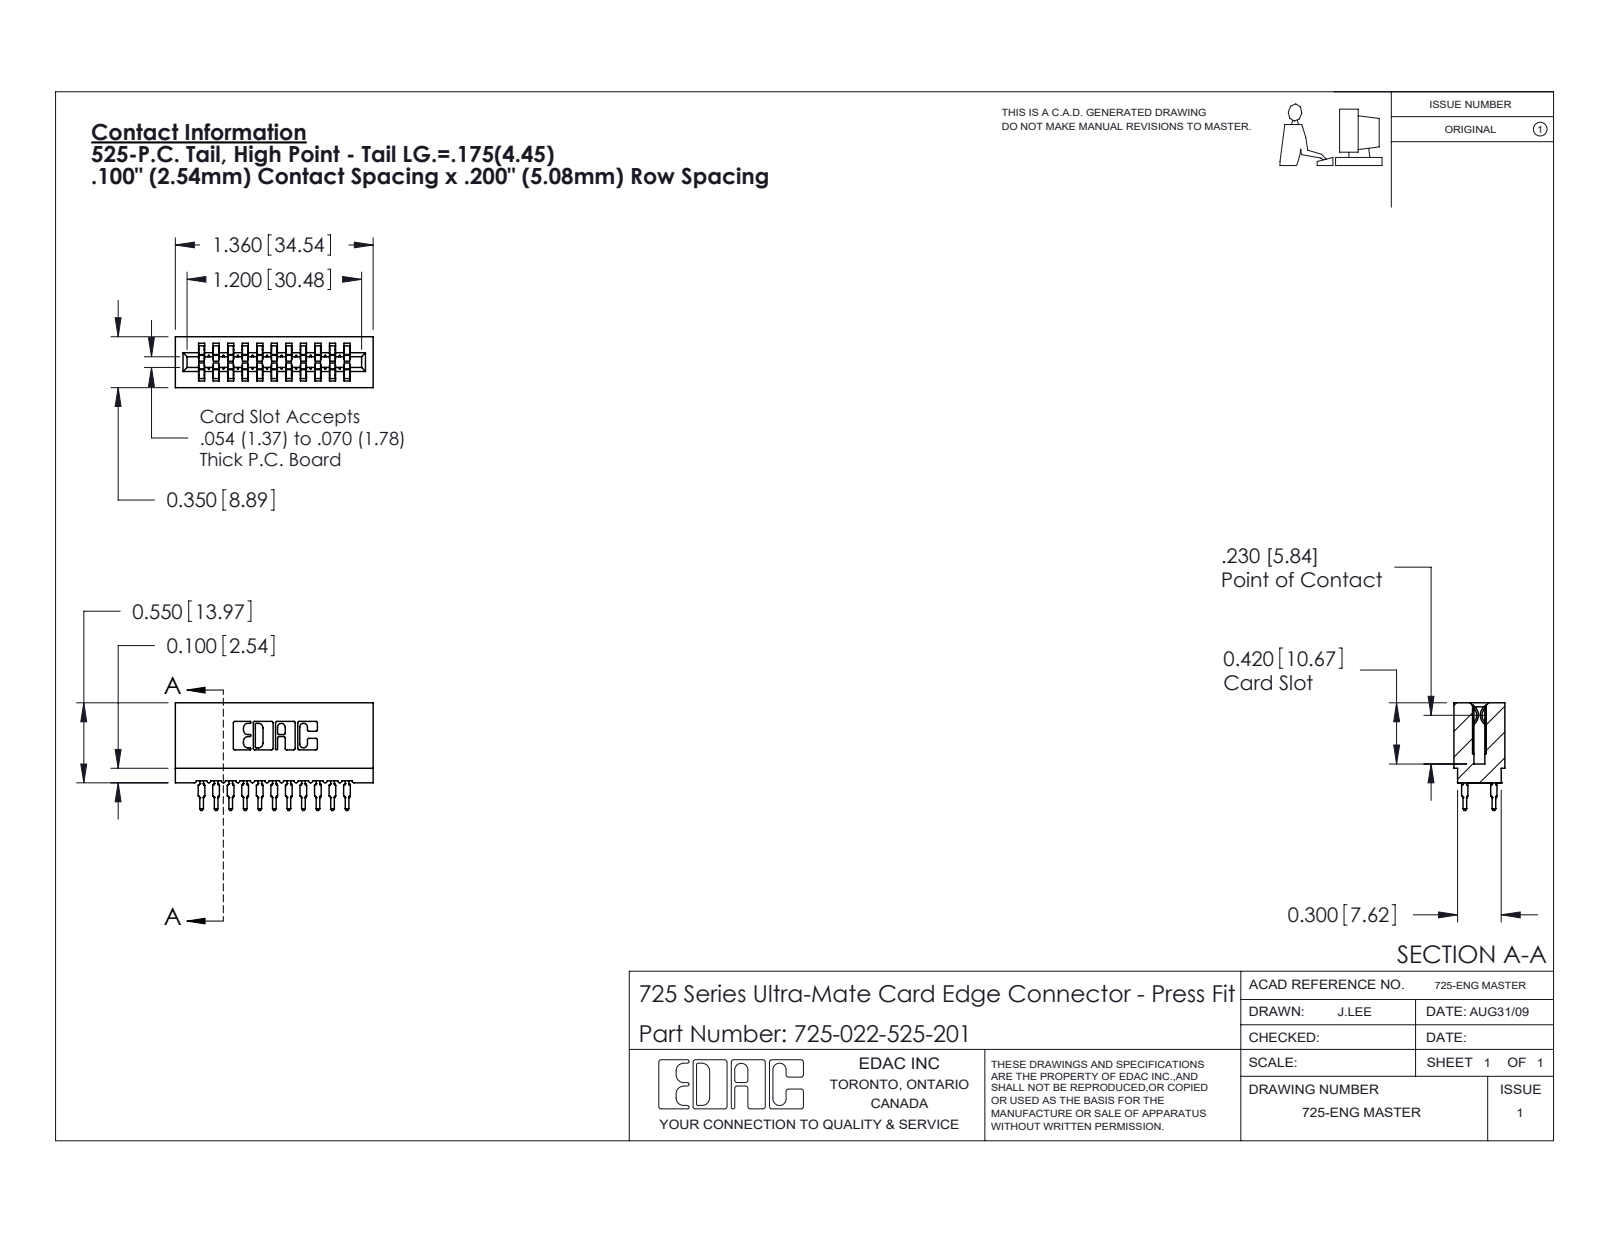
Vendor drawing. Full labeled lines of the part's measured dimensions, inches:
Part name (STEP PRODUCT): 725-022-525-201; 745-292-001_525; 725 Part_Insulator Option - 01
STEP written by: SolidWorks 2020 (CONFIG_CONTROL_DESIGN)
Units: inches
Bodies: 23 solids, 2064 faces (1067 planar, 425 cylindrical, 572 other)
Overall size (bounding box): 1.36 × 0.741 × 0.35
Volume: 0.176 in³ · Surface area: 8.412 in²
Partial cylindrical surfaces — rounded edges, fillets, slot ends (radius × count): R0.021 ×44, R0.01 ×22, R0.015 ×22, R0.005 ×8, R0.011 ×8, R0.007 ×6, R0.031 ×6, R0.026 ×3
Main face-to-face distances: 0.1, 0.2, 0.3, 0.4, 0.5, 0.158, 0.058, 0.042, 0.142, 0.258
